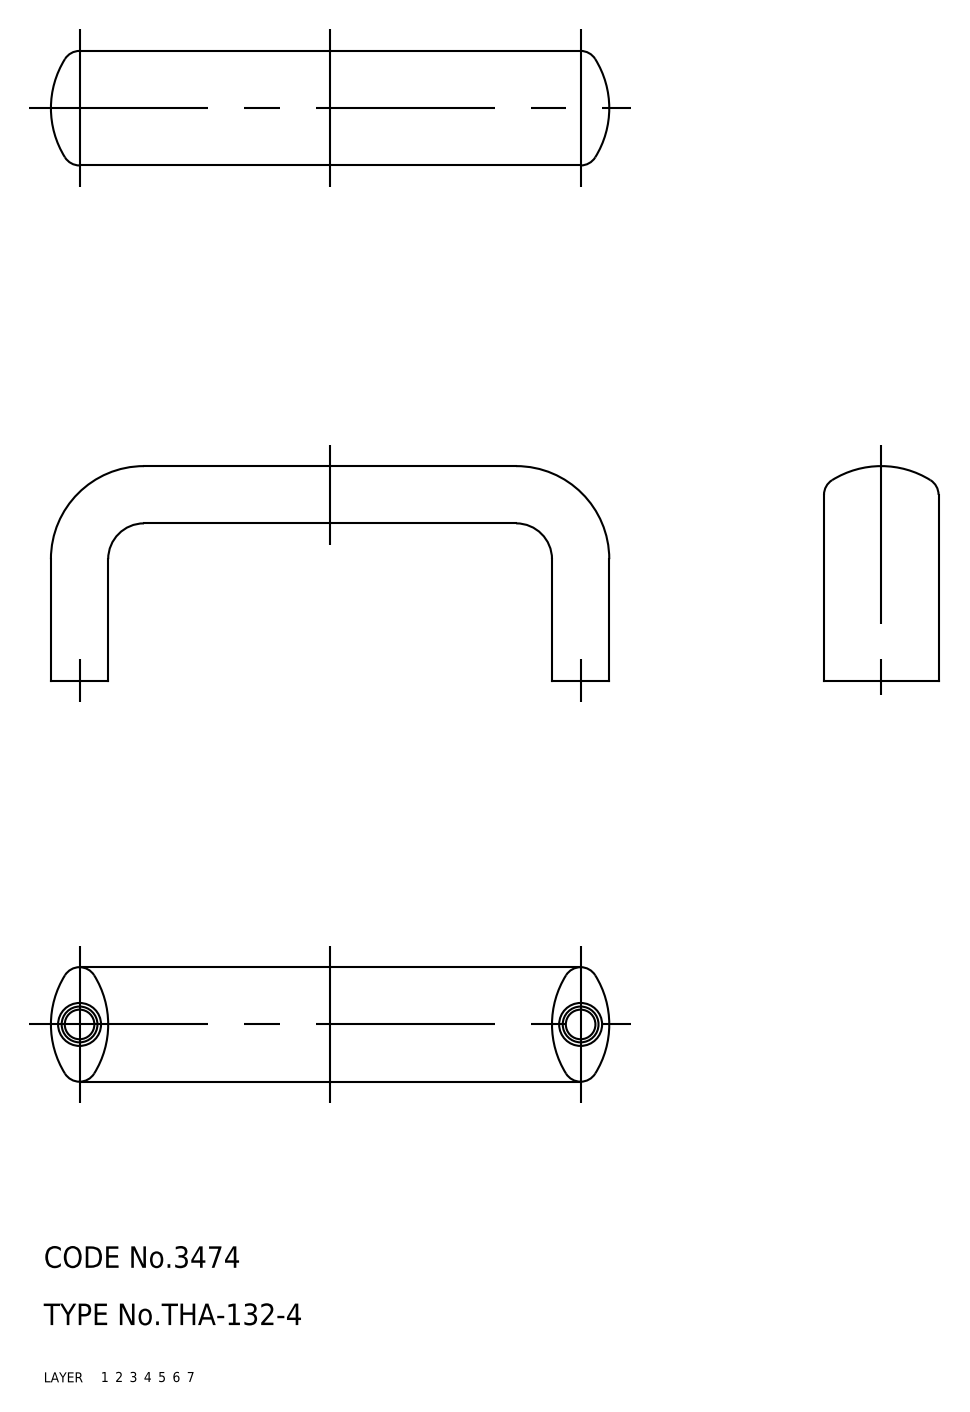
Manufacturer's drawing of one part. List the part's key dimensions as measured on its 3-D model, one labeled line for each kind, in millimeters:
Part name (STEP PRODUCT): pull
STEP written by: CADfix (AUTOMOTIVE_DESIGN)
Units: millimetres
Bodies: 1 solid, 28 faces (0 planar, 0 cylindrical, 28 other)
Overall size (bounding box): 78 × 30 × 16
Volume: 10 921 mm³ · Surface area: 4 933 mm²
